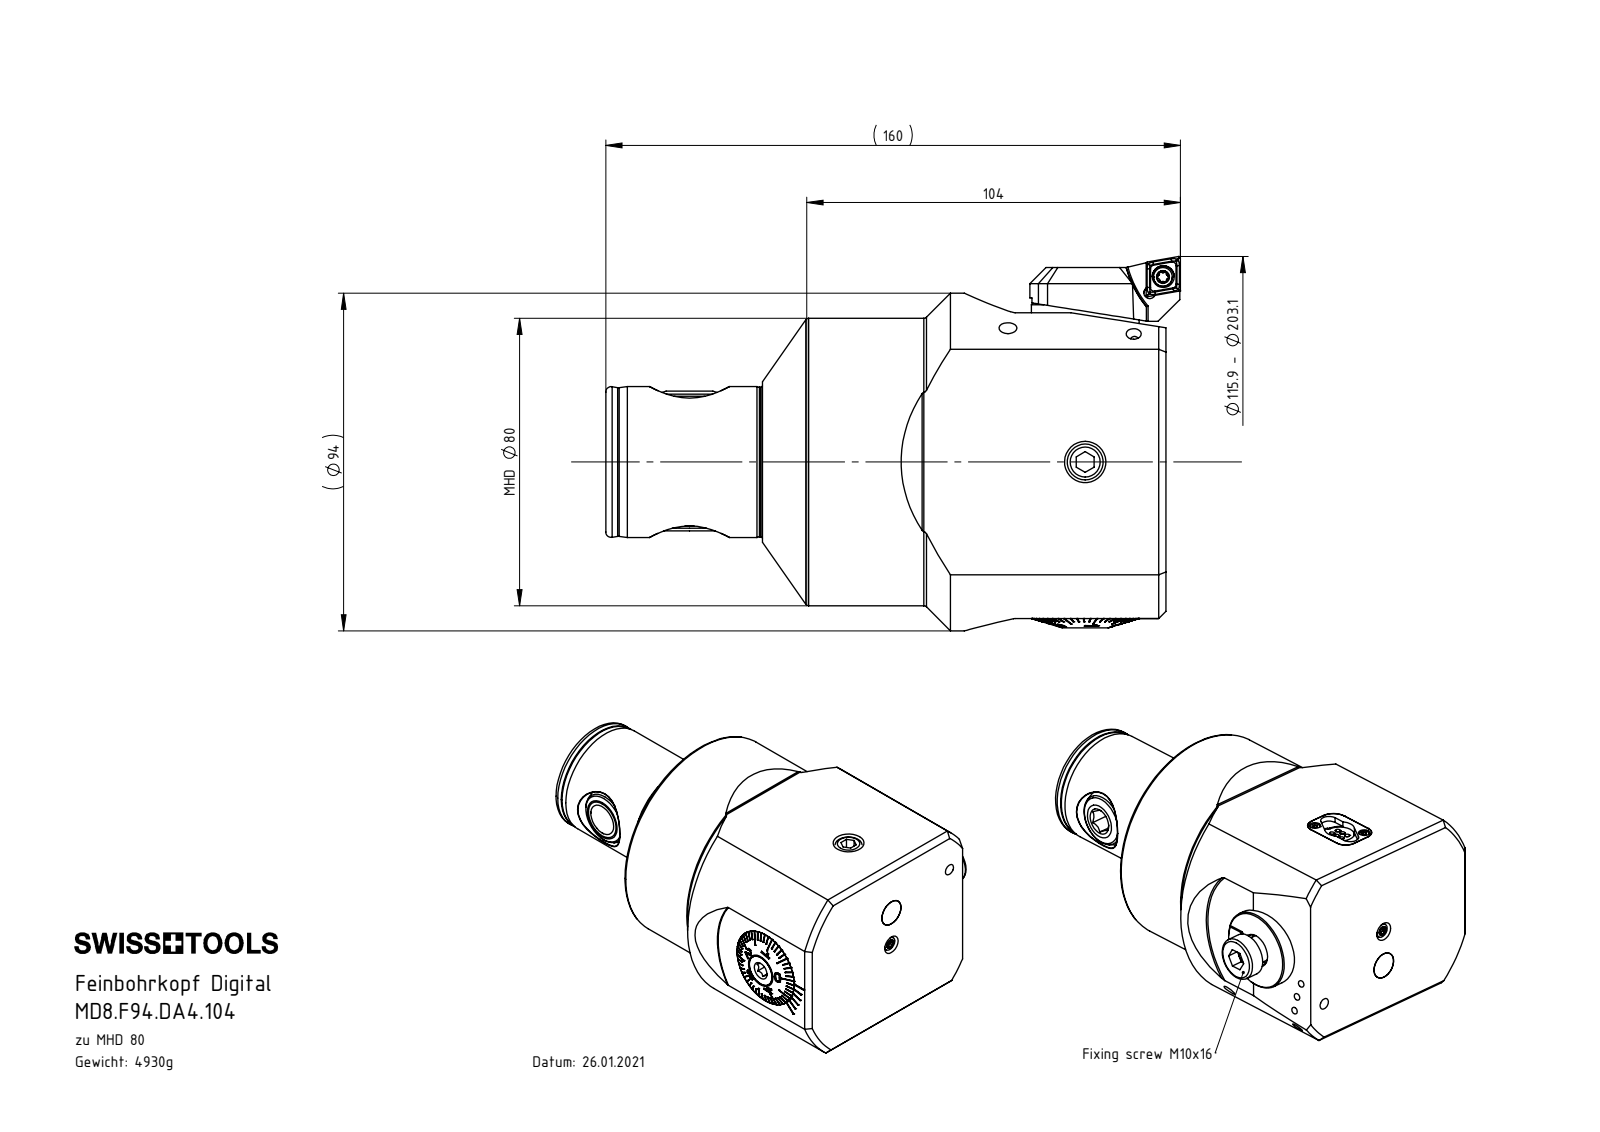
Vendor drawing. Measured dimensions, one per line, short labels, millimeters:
name: MD8-F94.DA3.104_A; DIN 3771 - 13x1; ISO 4762 - M2 x 4; ISO 4026 - M10 x 16 (+8 more)
written by: SolidWorks 2017 (AUTOMOTIVE_DESIGN)
unit: mm
bodies: 39 solids, 1280 faces (536 planar, 297 cylindrical, 447 other)
size: 159.98 × 104.2 × 80
volume: 631 171 mm³; area: 96 135 mm²
holes: 5× ⌀4.2, 4× ⌀3.3, 3× ⌀2.5, 3× ⌀8.5, 2× ⌀1.6, 2× ⌀2.2, 2× ⌀5, 2× ⌀8, 2× ⌀12, 2× ⌀12.5, 2× ⌀13, 1× ⌀4.4
bosses: 6× ⌀1.9, 2× ⌀10, 2× ⌀5.25, 2× ⌀4, 2× ⌀3.8, 2× ⌀2, 1× ⌀80, 1× ⌀42
rounds: 12× R0.34, 12× R0.59, 6× R1.1, 6× R1.2, 6× R2, 6× R2.5, 5× R0.5, 3× R3.2
face distances: 69, 155.98, 81.2, 87.7, 6.5, 2.6, 78.6, 85.1, 2.5, 4
hole spacings: 9.52, 1.21, 5.73, 5.86, 8.49, 10.59, 14.5, 19.04
